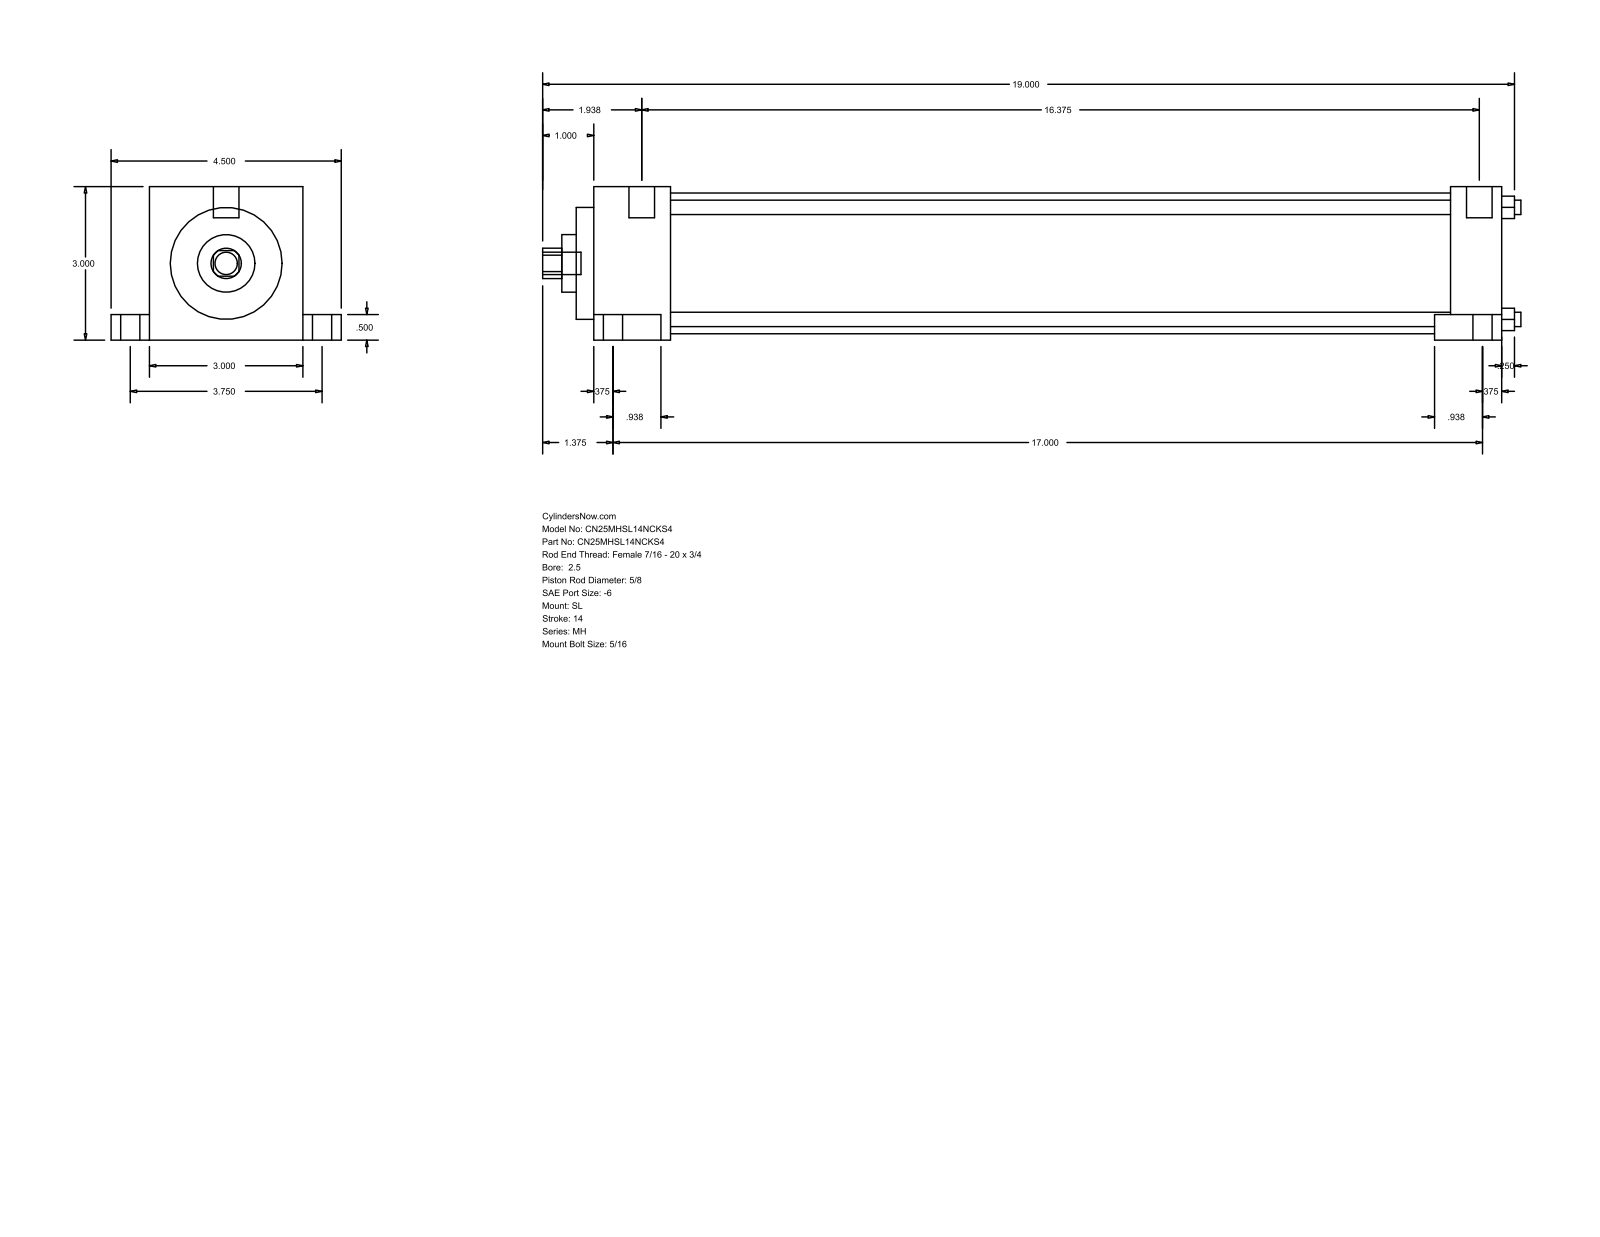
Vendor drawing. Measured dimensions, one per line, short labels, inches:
name: MH_SL__0250_0.625
written by: GSSL Pune (CONFIG_CONTROL_DESIGN)
unit: in
bodies: 0 solids, 86 faces (61 planar, 25 cylindrical, 0 other)
size: 19.125 × 4.5 × 3
holes: 4× ⌀0.281, 1× ⌀0.625, 1× ⌀1.125, 1× ⌀2.187, 1× ⌀2.75
bosses: 2× ⌀0.625, 2× ⌀0.375, 2× ⌀0.219, 1× ⌀0.5, 1× ⌀0.437
rounds: 1× R0.297
face distances: 3, 1, 17.094, 18.094, 0.5, 2.5, 0.75, 3.75, 18.375, 1.25
hole spacings: 1.548, 2.19, 3.097
